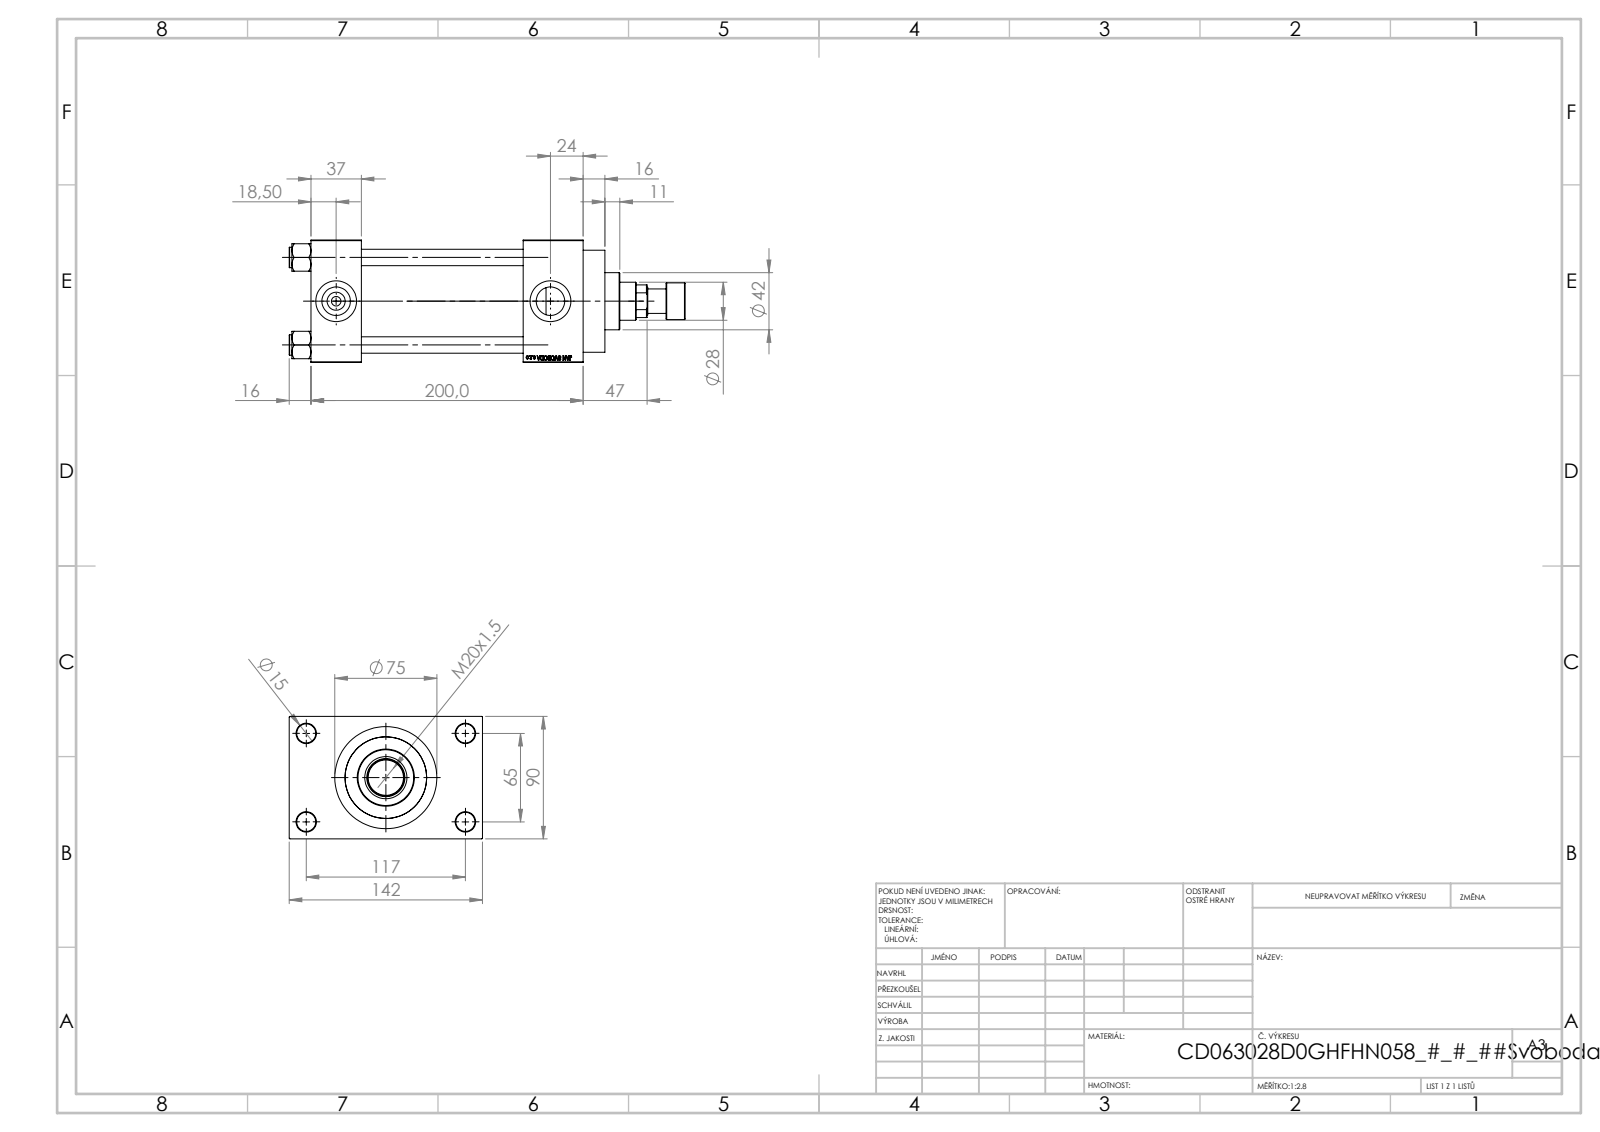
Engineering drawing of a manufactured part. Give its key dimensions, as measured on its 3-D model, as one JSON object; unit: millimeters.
{"part_name": "V215CD_D_Body; V215CD_D_TYCINKA; V215CD_VCP_D; V215CD_NUT_M5_D (+2 more)", "step_written_by": "SolidWorks 2019 (CONFIG_CONTROL_DESIGN)", "units": "millimeters", "bodies": {"solids": 12, "faces": 1117, "planar": 501, "cylindrical": 92, "other": 524}, "overall_size": [291, 142, 90], "volume_mm3": 1209000, "surface_area_mm2": 242777, "round_holes": [[12, 4], [14, 4], [7, 2], [20.96, 2], [30, 2], [18.5, 1], [28, 1], [31, 1], [50, 1], [60, 1], [63, 1]], "round_bosses_or_shafts": [[15, 4], [75, 1], [69, 1], [42, 1], [27, 1], [18, 1]], "face_to_face_distances": [90, 119, 37, 156, 163, 200, 44, 26, 116, 16], "hole_center_spacings": [26.35, 45.47, 64.3, 66.92, 69.81, 90.65, 111.34, 65]}
